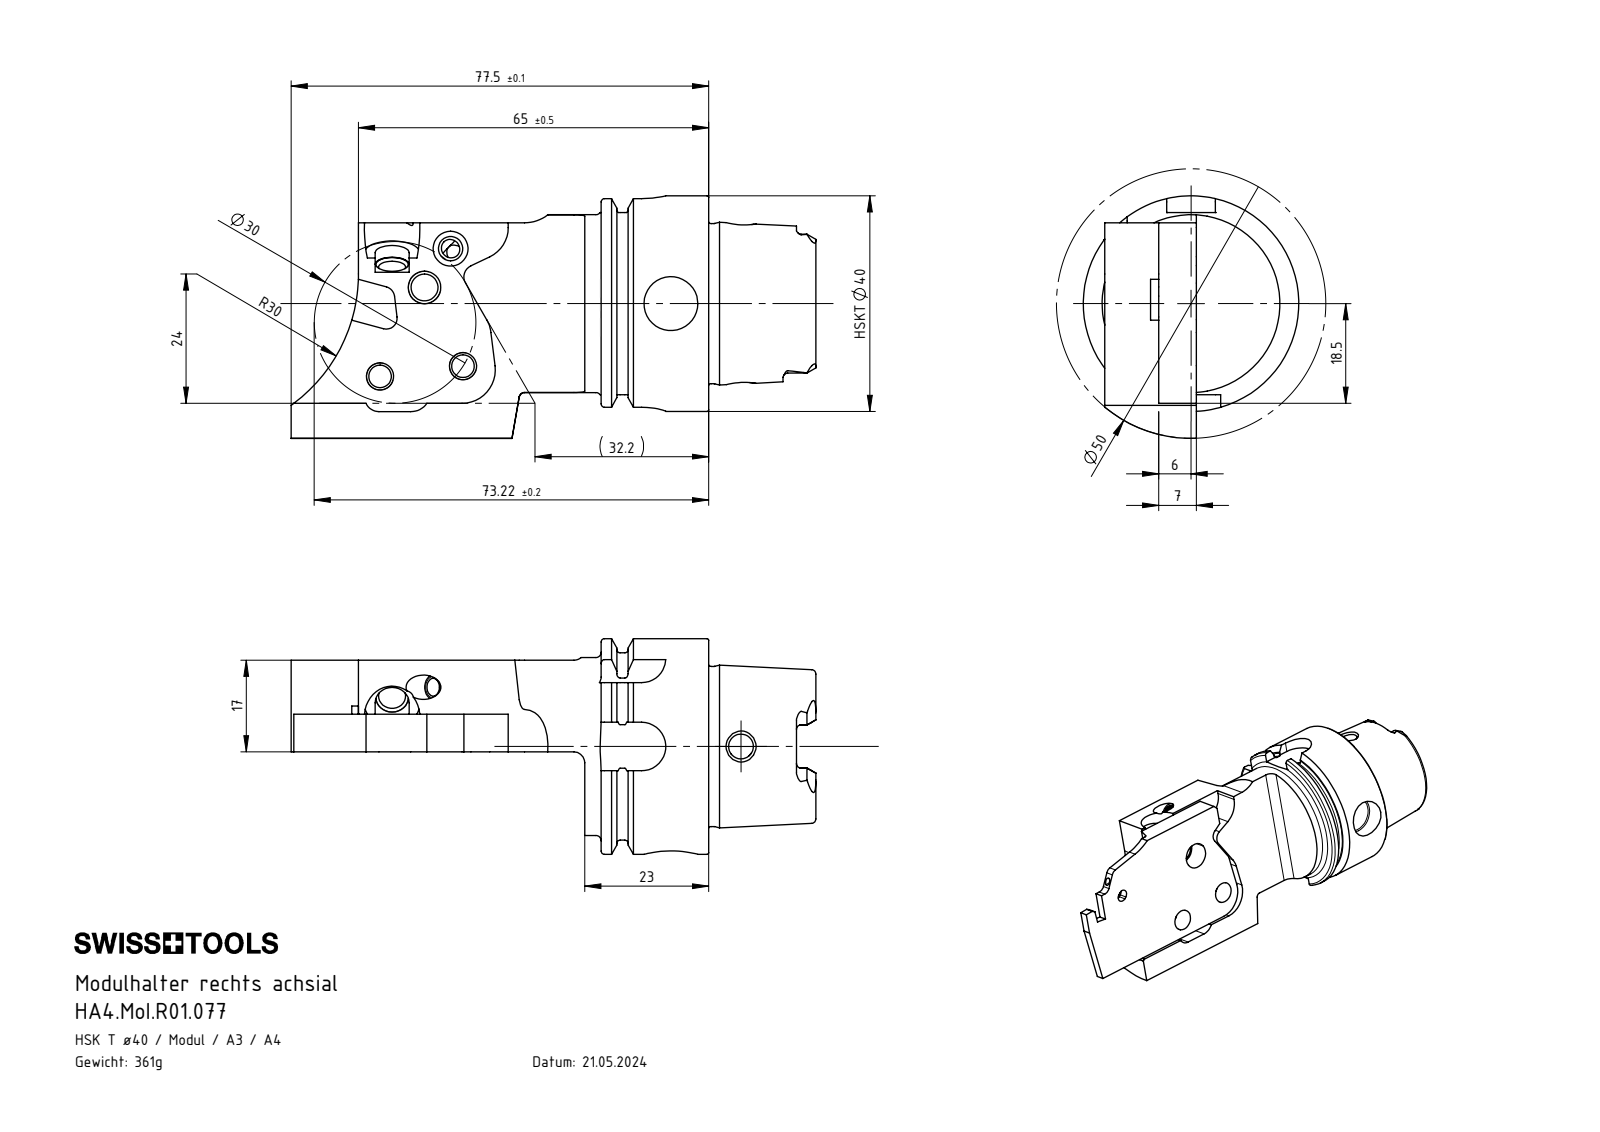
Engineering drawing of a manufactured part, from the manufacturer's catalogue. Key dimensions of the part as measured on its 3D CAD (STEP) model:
Part name (STEP PRODUCT): HA4.MoI.R01.077; ISO 4026 - M4 x 4; DIN 3771 - 5x1; HA4-MoI.R01.077_B (+1 more)
STEP written by: SolidWorks 2022 (AUTOMOTIVE_DESIGN)
Units: millimetres
Bodies: 6 solids, 306 faces (101 planar, 105 cylindrical, 100 other)
Overall size (bounding box): 97.4 × 45 × 40
Volume: 45 818 mm³ · Surface area: 16 955 mm²
Round holes (diameter × count): ⌀3.3 ×5, ⌀4.5 ×3, ⌀5 ×3, ⌀4.2 ×2, ⌀6.96 ×2, ⌀4.6 ×1, ⌀10 ×1, ⌀11 ×1, ⌀12.5 ×1, ⌀21 ×1, ⌀25.5 ×1
Round bosses / shafts (diameter × count): ⌀4 ×3, ⌀4.66 ×2, ⌀40 ×1, ⌀34.75 ×1, ⌀33 ×1, ⌀29.71 ×1
Partial cylindrical surfaces — rounded edges, fillets, slot ends (radius × count): R0.9 ×6, R1.88 ×4, R2 ×4, R4.5 ×4, R0.2 ×3, R7 ×3, R6.2 ×2, R2.3 ×1
Main face-to-face distances: 17, 10, 7, 23, 7.95, 15.05, 12, 19.95, 3.05, 19.9
Hole centre spacings: 7.01, 8.68, 10.4, 12.84, 14.89, 15.42, 16.48, 18.54
